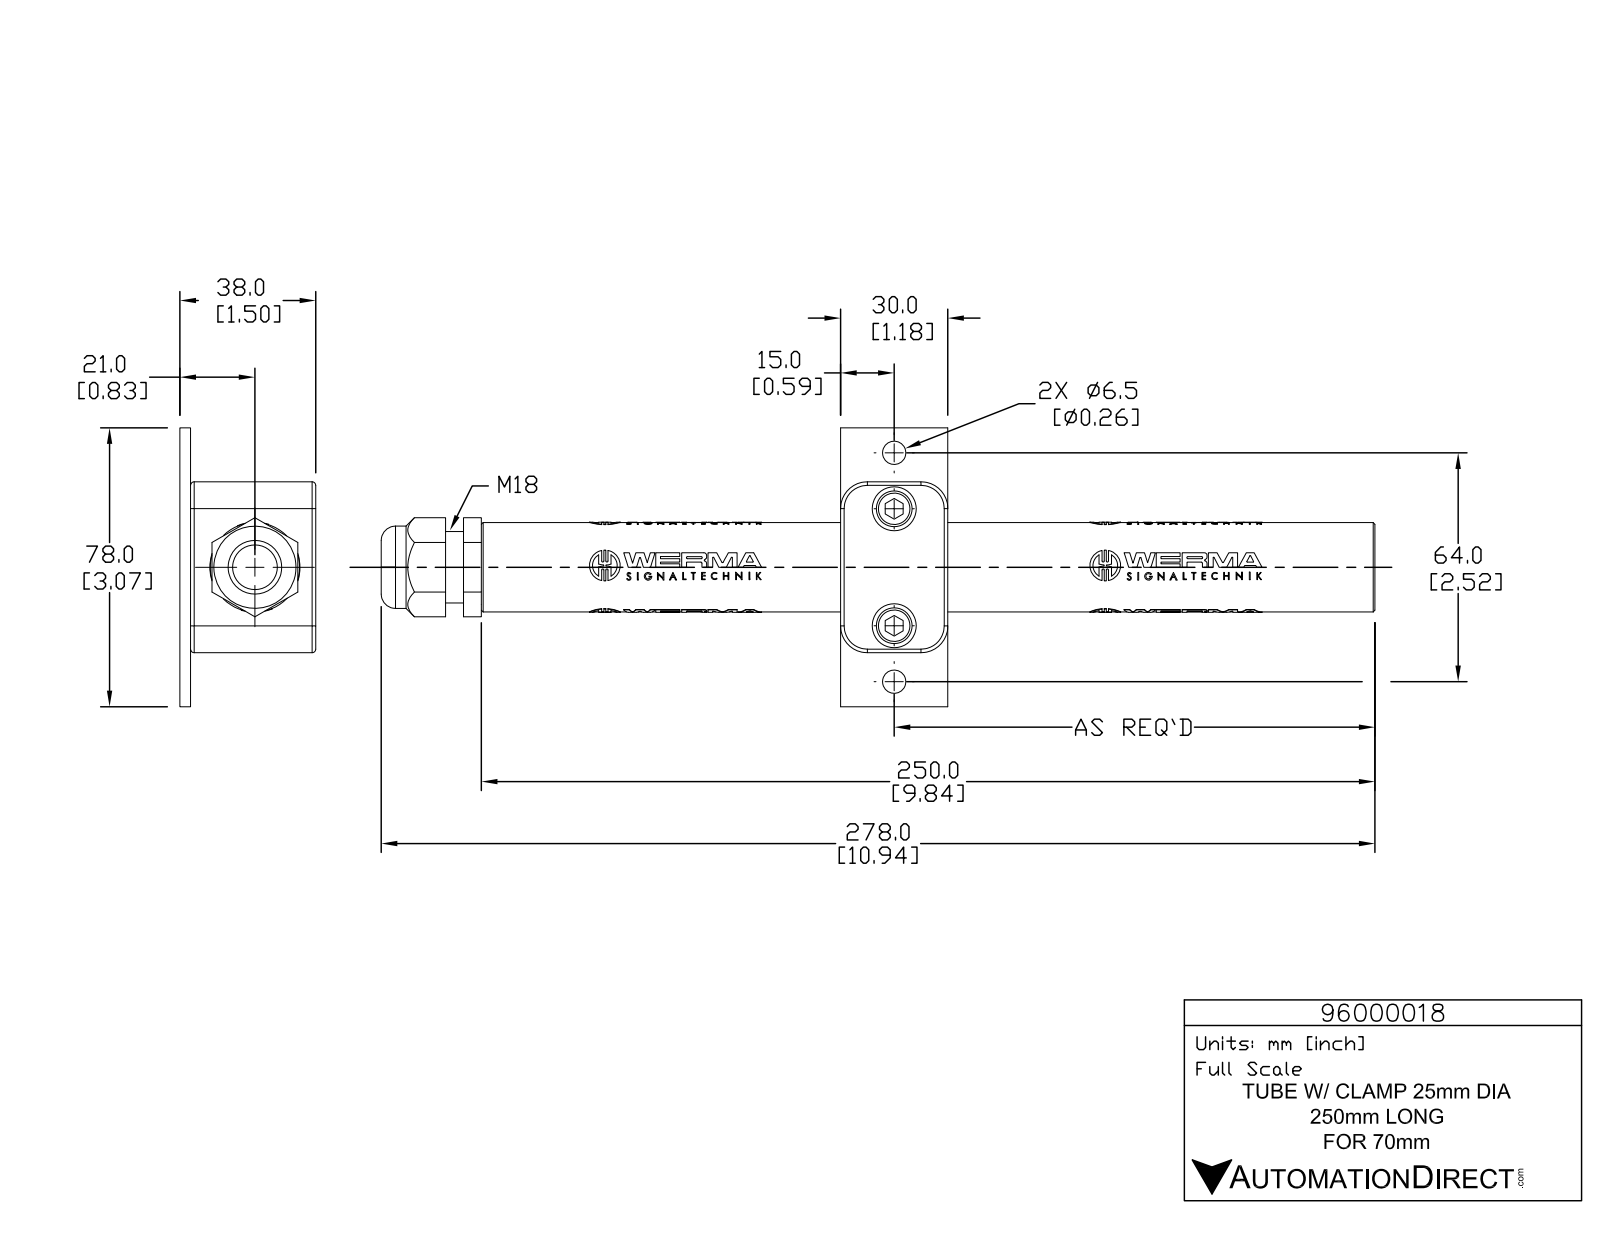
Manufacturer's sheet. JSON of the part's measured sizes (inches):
{"part_name": "96000018", "step_written_by": "SolidWorks 2015 (AUTOMOTIVE_DESIGN)", "units": "inches", "bodies": {"solids": 1, "faces": 2159, "planar": 1436, "cylindrical": 699, "other": 24}, "overall_size": [10.945, 3.071, 1.496], "volume_in3": 6.568, "surface_area_in2": 72.04, "round_holes": [[0.059, 8], [0.256, 2], [0.484, 2], [0.492, 1], [0.591, 1], [0.709, 1], [0.723, 1]], "round_bosses_or_shafts": [[0.339, 8], [0.084, 8], [0.394, 2], [0.984, 1], [0.906, 1], [0.787, 1]], "partial_cylinders_radius": [[0.005, 24], [0.005, 16], [0.012, 16], [0.012, 16], [0.012, 16], [0.196, 16], [0.005, 8], [0.005, 8]], "face_to_face_distances": [1.181, 0.118, 1.378, 1.496, 0.945, 1.882, 0.197, 4.705, 0.236, 0.354], "hole_center_spacings": [0.198, 5.512, 5.515, 0.616, 1.904, 2.766, 2.811, 2.853]}
